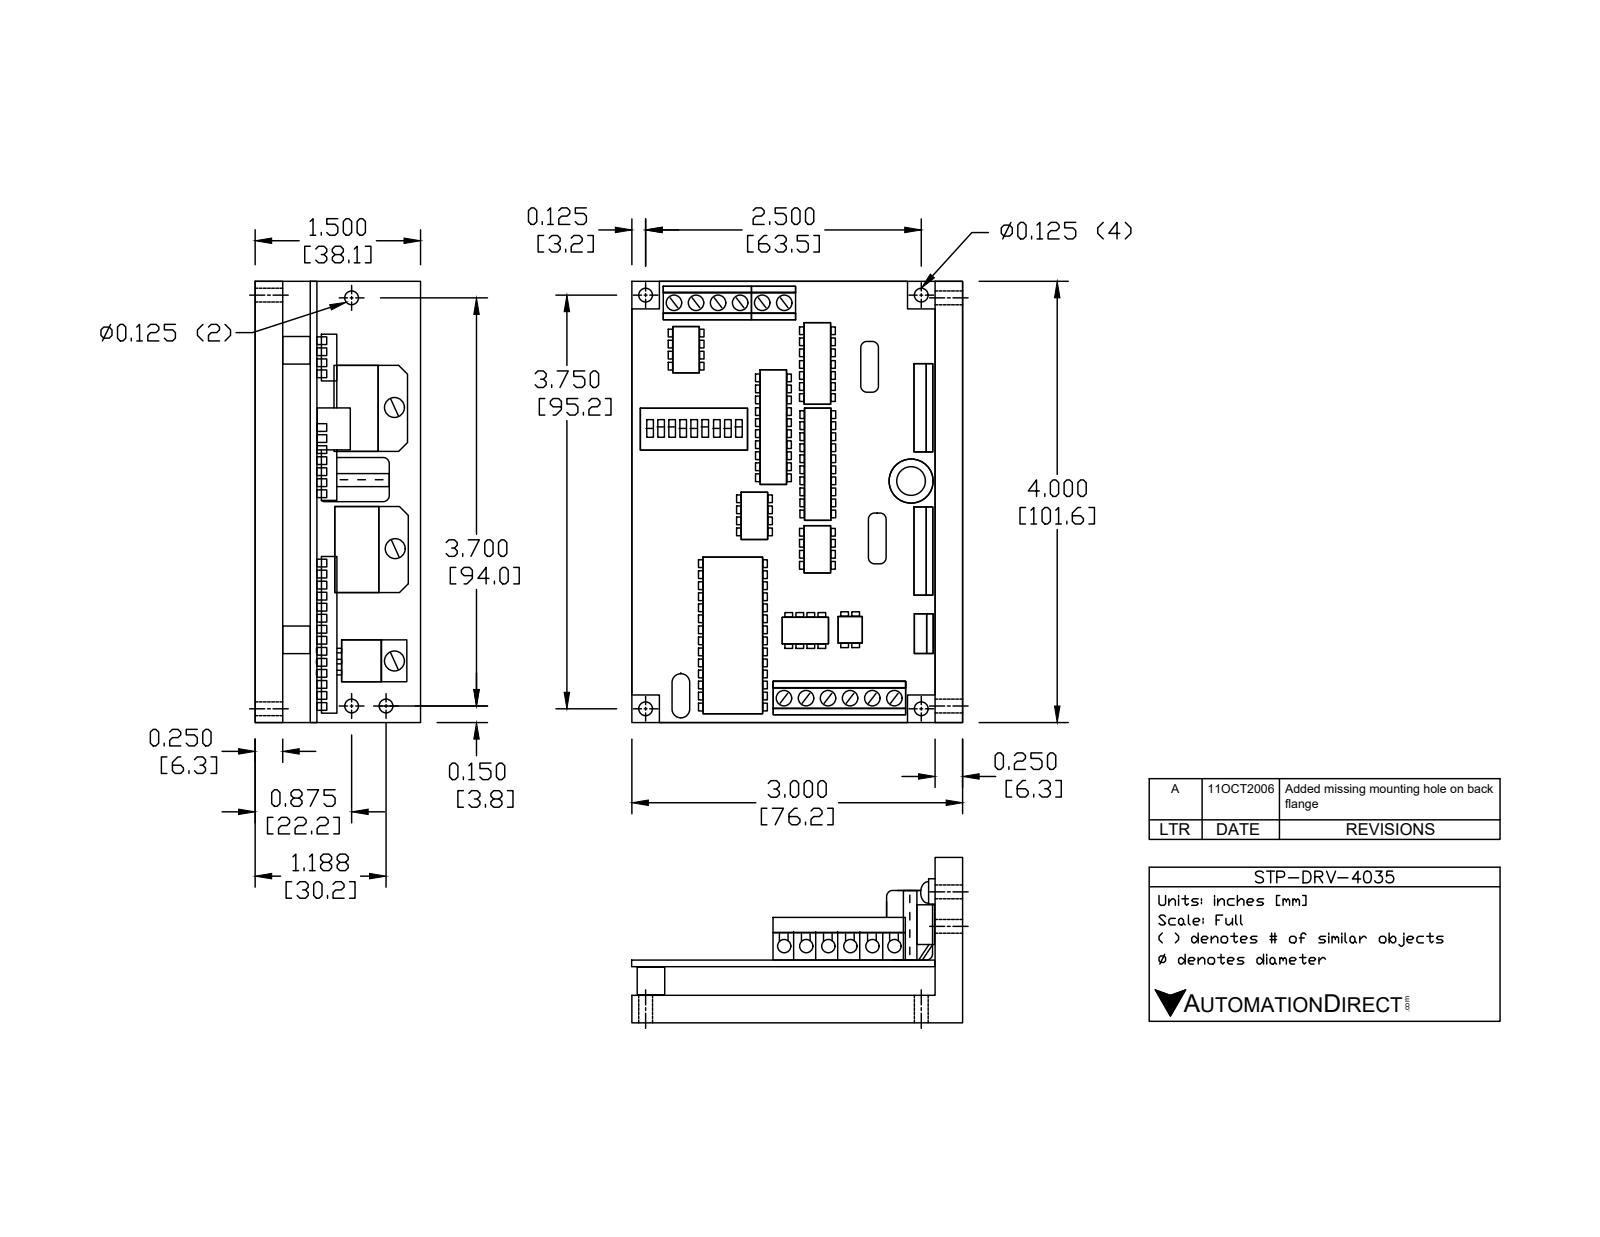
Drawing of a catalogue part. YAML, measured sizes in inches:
part_name: "STP-DRV-4035"
step_written_by: "SolidWorks 2014 (AUTOMOTIVE_DESIGN)"
units: inches
bodies: {solids: 1, faces: 115, planar: 71, cylindrical: 42, other: 2}
overall_size: [4, 3, 1.5]
volume: 5.948
surface_area: 67.35
round_holes:
  - {diameter: 0.125, count: 6}
round_bosses_or_shafts:
  - {diameter: 0.26, count: 2}
  - {diameter: 0.4, count: 1}
partial_cylinders:
  - {radius: 0.05, count: 10}
  - {radius: 0.025, count: 2}
face_to_face_distances: [0.25, 0.51, 0.26, 0.572, 0.322, 0.062, 2.75, 1.5, 1.25, 2.575]
hole_center_spacings: [2.5, 3.75, 4.507, 3.7]
